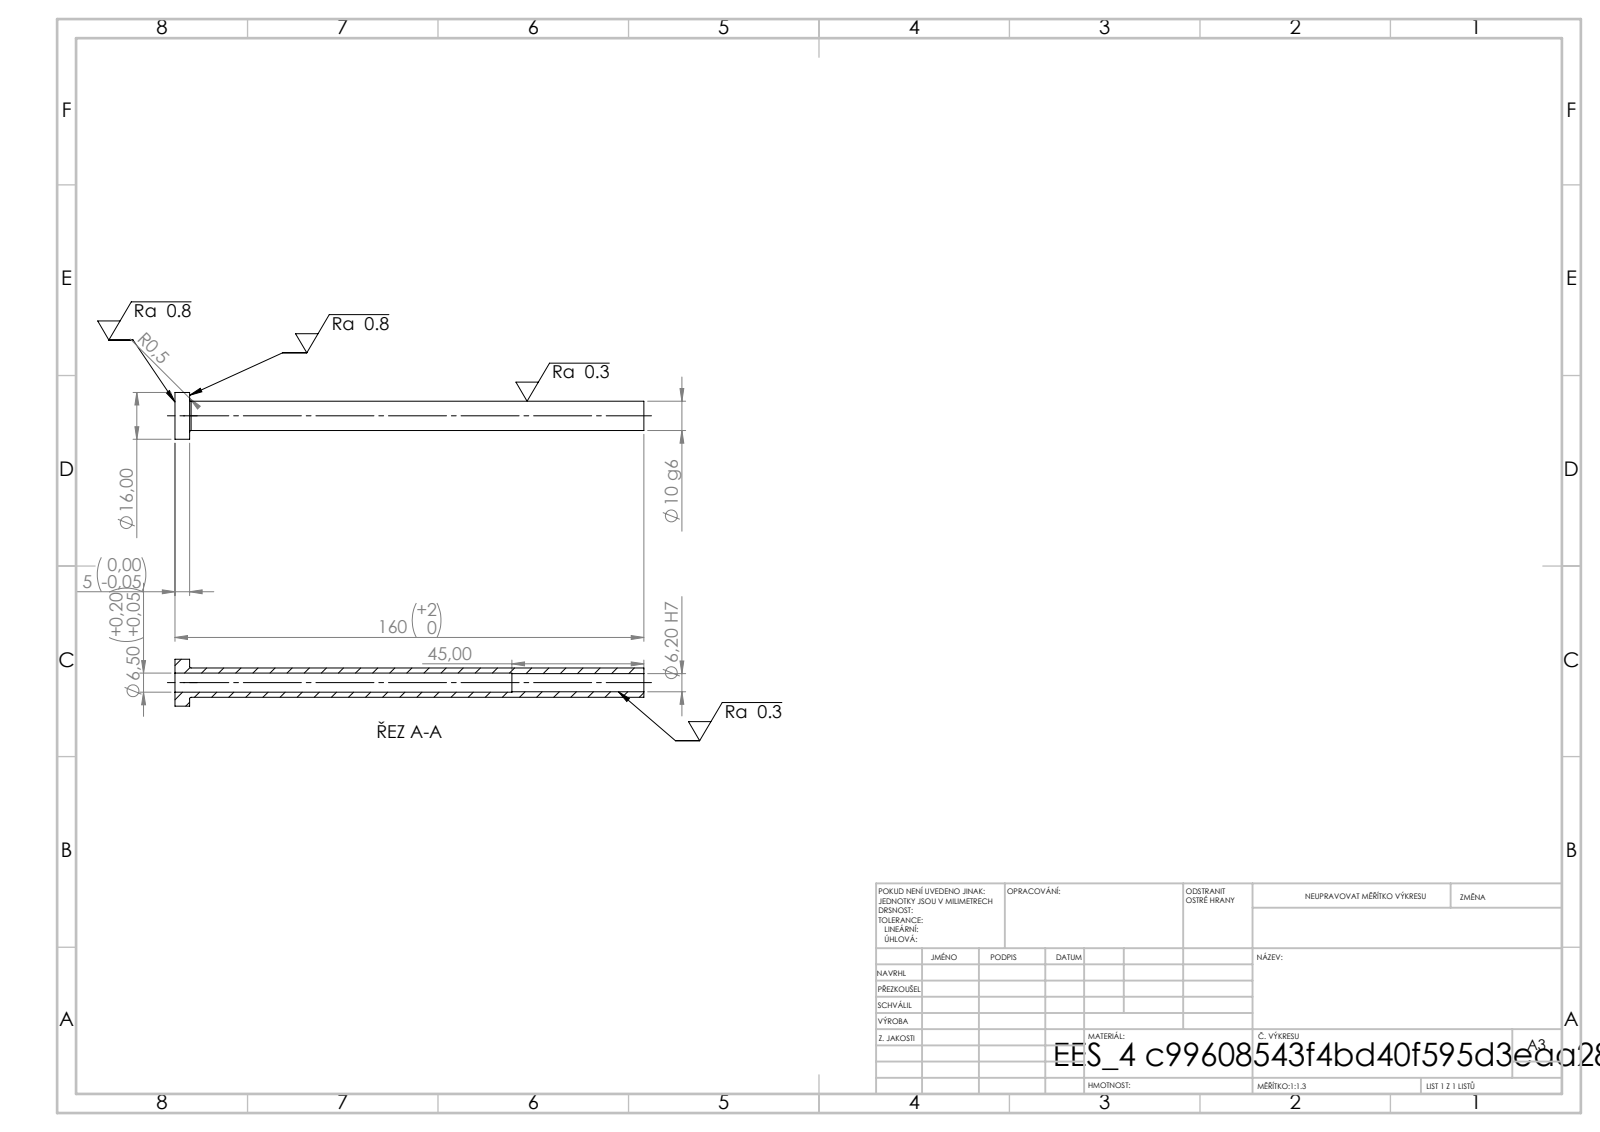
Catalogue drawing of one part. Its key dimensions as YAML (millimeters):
step_written_by: "SolidWorks 2019 (CONFIG_CONTROL_DESIGN)"
units: millimeters
bodies: {solids: 1, faces: 14, planar: 4, cylindrical: 8, other: 2}
overall_size: [160, 16, 16]
volume: 8006
surface_area: 8681
round_holes:
  - {diameter: 6.2, count: 1}
  - {diameter: 6.5, count: 1}
round_bosses_or_shafts:
  - {diameter: 16, count: 1}
  - {diameter: 10, count: 1}
face_to_face_distances: [5, 160, 155, 115, 110, 45]
